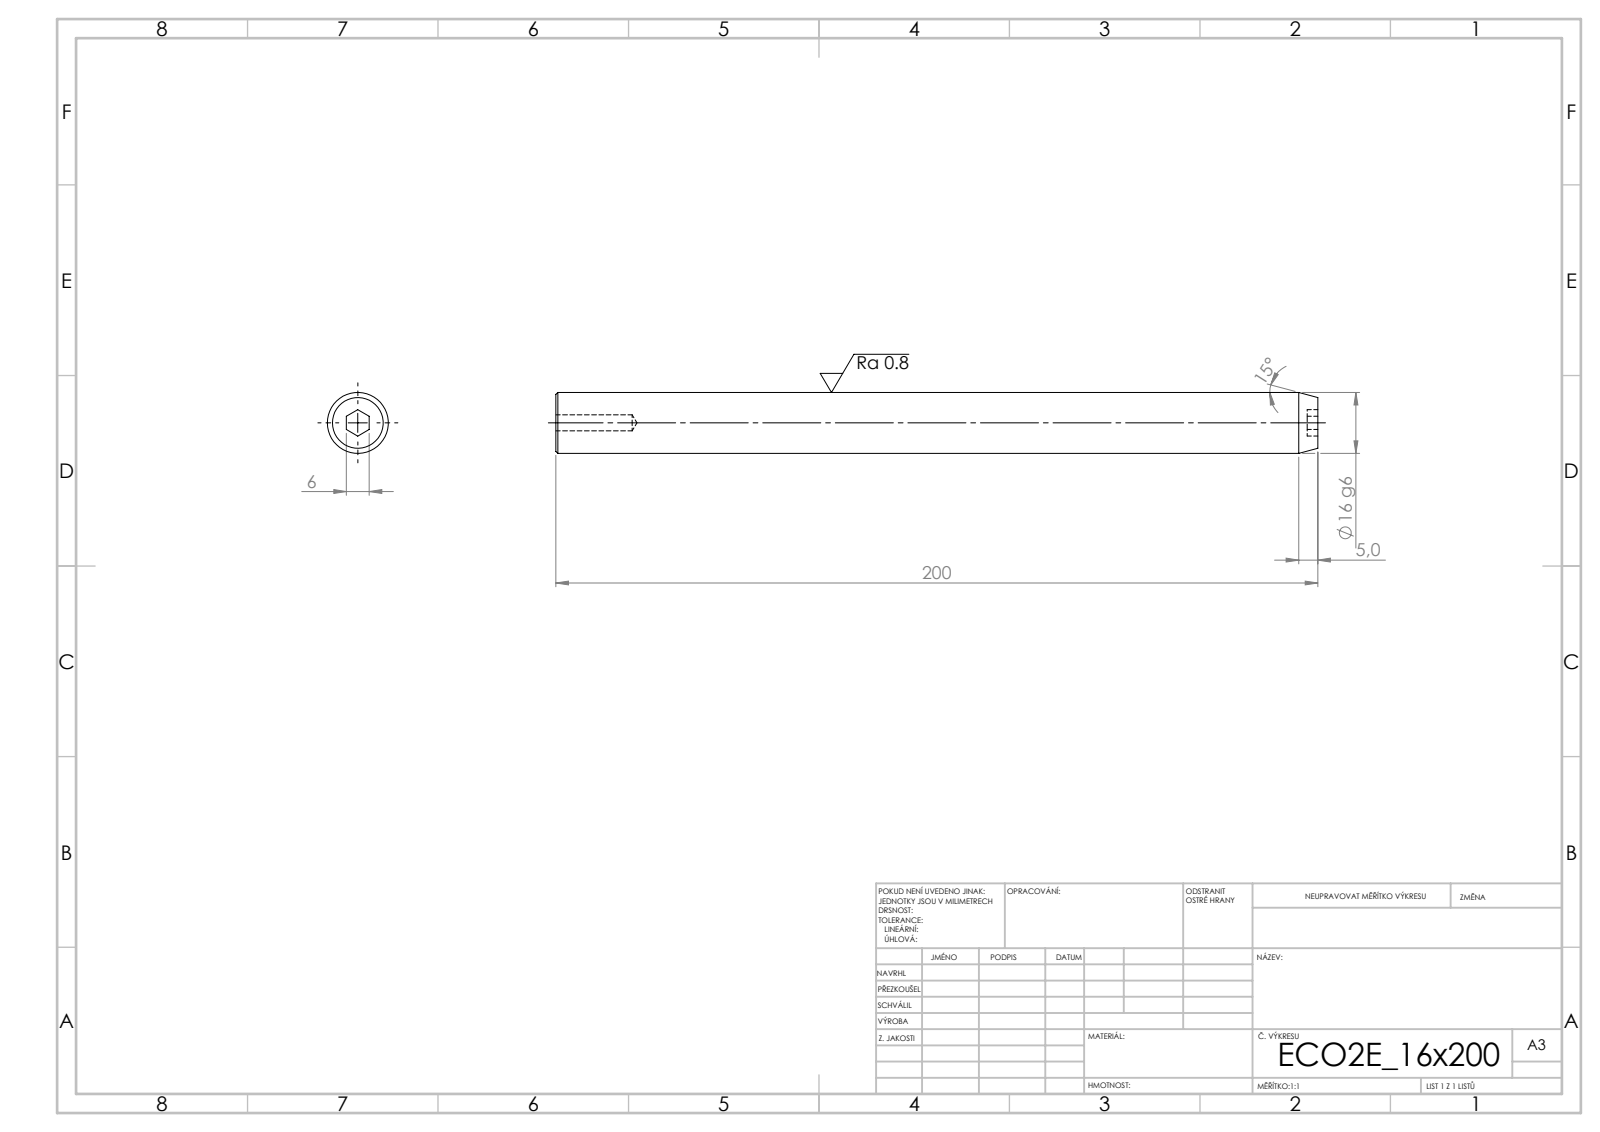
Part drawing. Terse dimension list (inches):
written by: SolidWorks 2019 (CONFIG_CONTROL_DESIGN)
unit: in
bodies: 1 solid, 19 faces (9 planar, 4 cylindrical, 6 other)
size: 7.874 × 0.63 × 0.63
volume: 2.421 in³; area: 16.57 in²
holes: 1× ⌀0.165
bosses: 1× ⌀0.63
face distances: 7.874, 0.11, 7.764, 0.236
